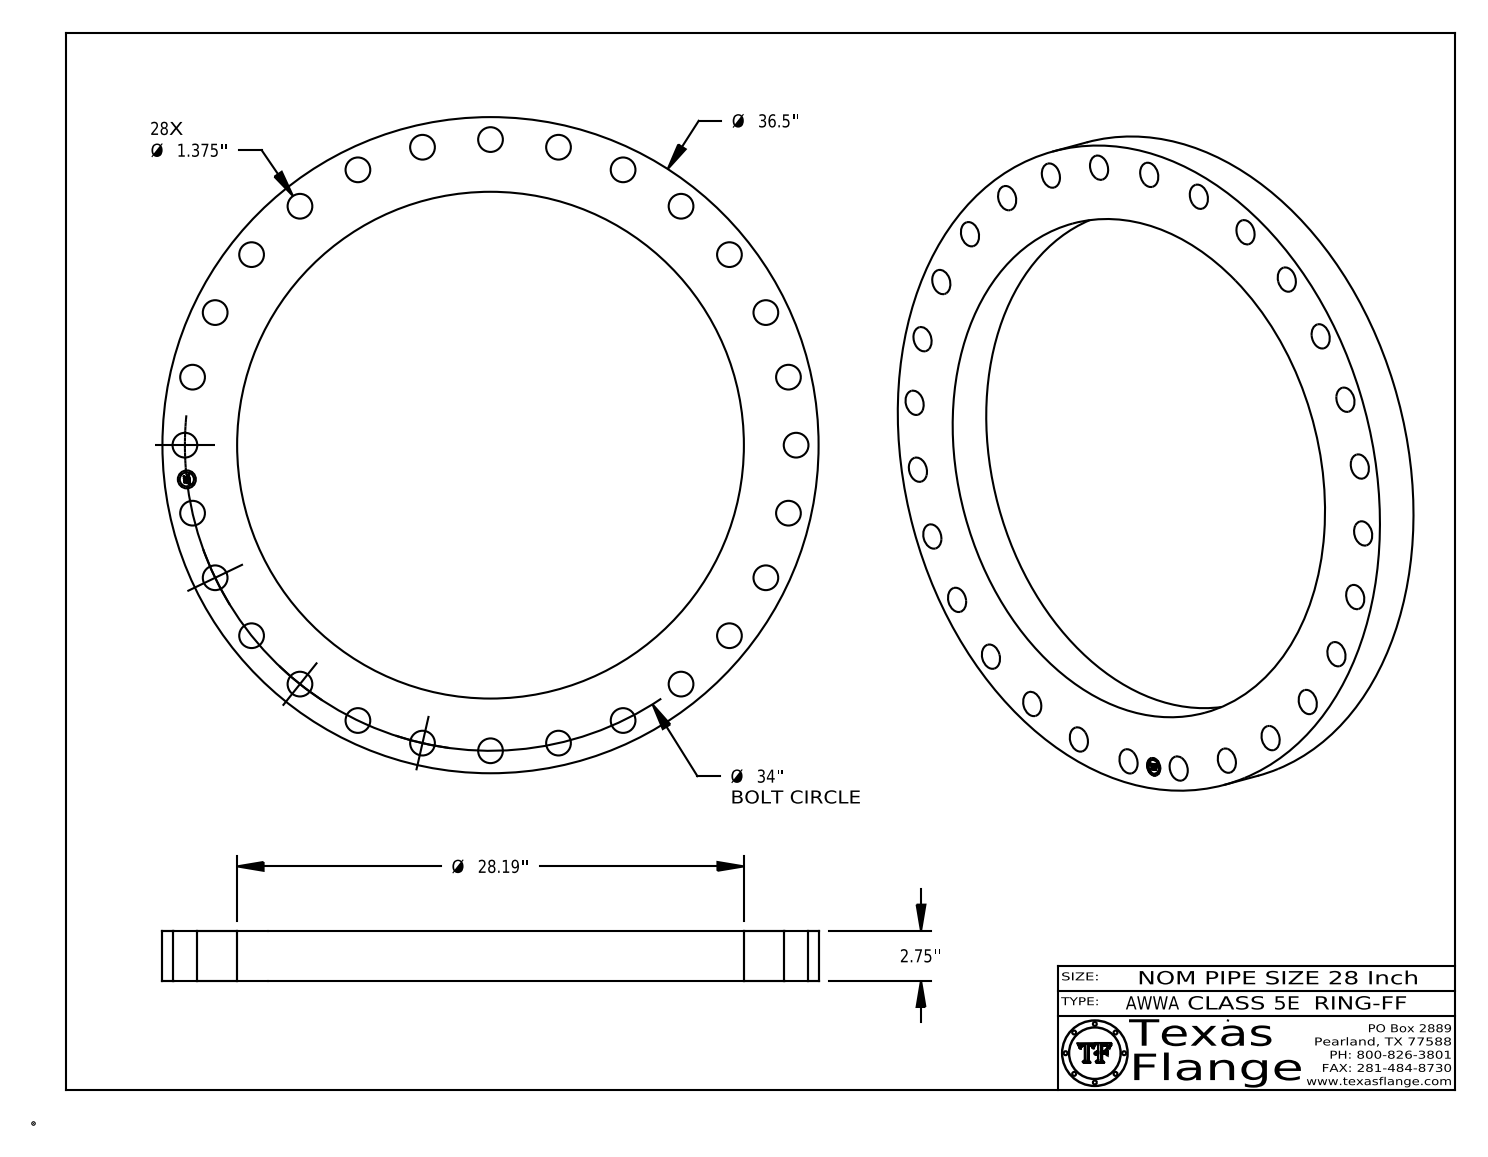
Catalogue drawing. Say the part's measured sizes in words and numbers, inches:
The part is named "AWWA Class 5E-RING-FF". Its 3-D file was written by "CATIA V5 STEP AP214 (AUTOMOTIVE_DESIGN)". It is 1 solid with 447 faces: 367 planar, 80 cylindrical and 0 other. Overall it measures 36.5 by 36.5 by 2.75 inches. Its volume is 1 047 cubic inches and its surface area 1 653 square inches. Round holes: 28 of diameter 1.375, 1 of diameter 1, 1 of diameter 28.19. Round bosses or shafts: 8 of diameter 0.061, 1 of diameter 36.5, 1 of diameter 0.788. The main face-to-face distances are 2.75, 0.015, 2.735, 0.298, 0.293, 0.054, 0.193, 0.248, 0.044, 0.15. The hole center spacings are 3.807, 7.566, 30.633, 33.786, 17, 11.23, 18.089, 21.198.
